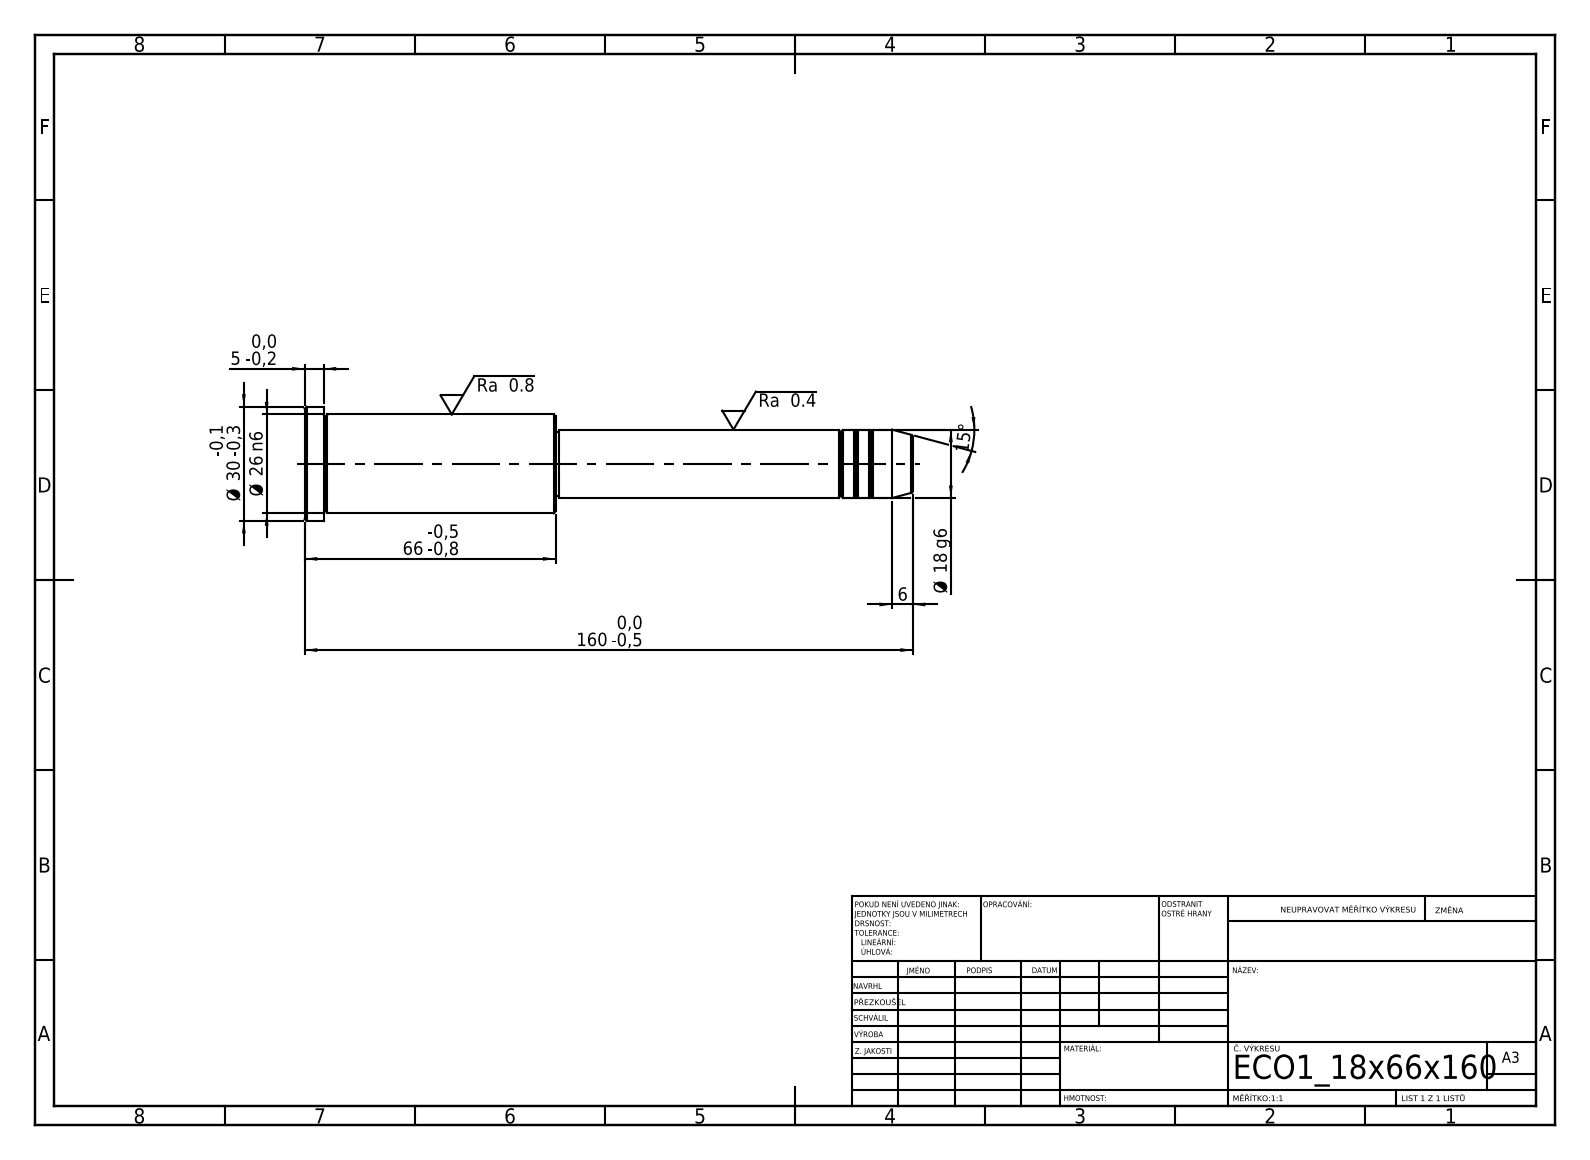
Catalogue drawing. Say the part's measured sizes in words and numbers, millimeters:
Its 3-D file was written by "SolidWorks 2019 (CONFIG_CONTROL_DESIGN)". It is 1 solid with 43 faces: 5 planar, 14 cylindrical and 24 other. Overall it measures 160 by 30 by 30 millimeters. Its volume is 59 477 cubic millimeters and its surface area 12 216 square millimeters. Round bosses or shafts: 1 of diameter 30, 1 of diameter 26, 1 of diameter 18, 1 of diameter 17. The main face-to-face distances are 66, 61, 5, 94, 155, 160, 93, 1, 62, 67.
